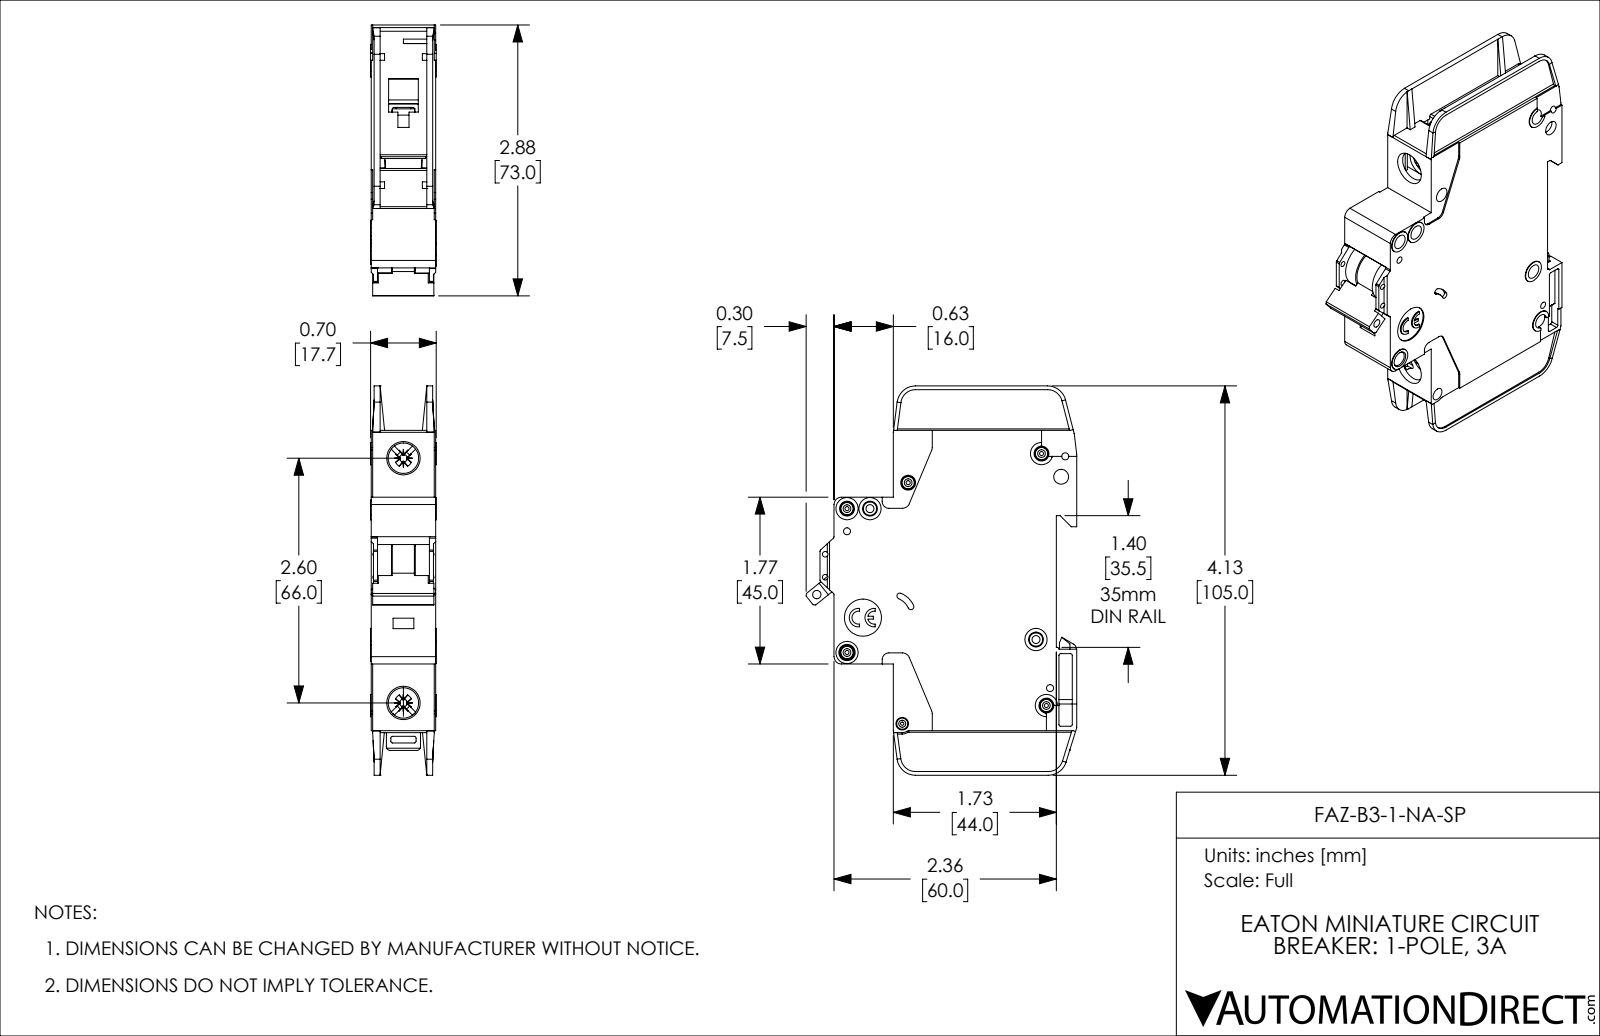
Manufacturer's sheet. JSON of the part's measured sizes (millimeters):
{"part_name": "FAZ-B3-1-NA-SP", "step_written_by": "SolidWorks 2019 (AUTOMOTIVE_DESIGN)", "units": "millimeters", "bodies": {"solids": 1, "faces": 1127, "planar": 671, "cylindrical": 357, "other": 99}, "overall_size": [105, 73.1, 17.7], "volume_mm3": 76720, "surface_area_mm2": 26460, "round_holes": [[4, 8], [1.1, 5], [1.9, 4], [1.5, 2], [2.2, 2], [8.2, 2], [0.9, 1], [2.3, 1], [2.5, 1], [3.4, 1], [10, 1]], "round_bosses_or_shafts": [[3.3, 5], [6, 4], [3, 2], [2.5, 1]], "partial_cylinders_radius": [[0.5, 42], [0.4, 10], [1, 10], [2, 8], [5, 5], [0.2, 4], [0.7, 4], [1.1, 4]], "face_to_face_distances": [1.2, 17.4, 15, 16.2, 2.4, 13.8, 0.4, 0.8, 12.6, 14.6], "hole_center_spacings": [6.2, 13.6, 22.1, 4.8, 5.1, 5.2, 5.6, 6.1]}
